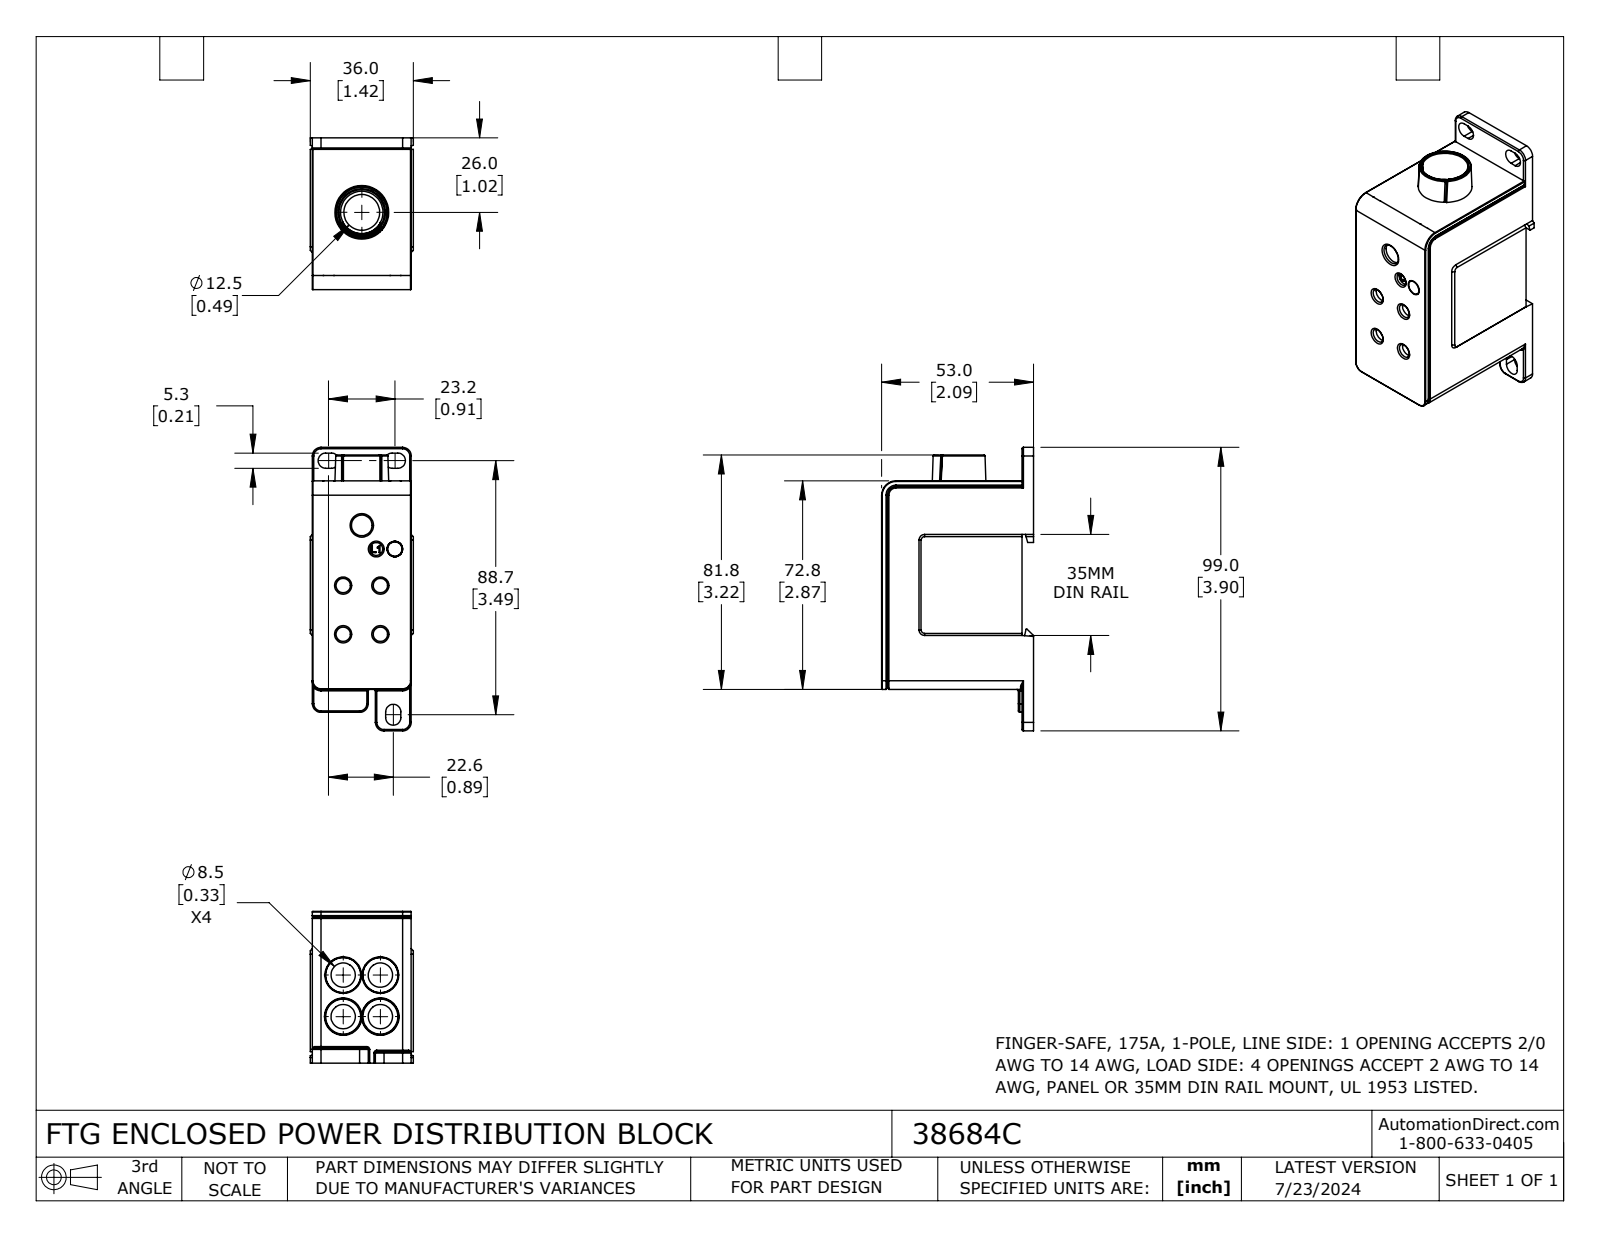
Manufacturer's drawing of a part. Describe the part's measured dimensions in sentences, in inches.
The part is named "38684C". Its 3-D file was written by "SolidWorks 2023 (CONFIG_CONTROL_DESIGN)". It is 1 solid with 276 faces: 92 planar, 72 cylindrical and 112 other. Overall it measures 3.898 by 2.087 by 1.417 inches. Its volume is 7.104 cubic inches and its surface area 39.29 square inches. Round holes: 4 of diameter 0.197, 4 of diameter 0.335, 1 of diameter 0.177, 1 of diameter 0.201, 1 of diameter 0.213, 1 of diameter 0.283, 1 of diameter 0.492, 1 of diameter 0.583. Round bosses or shafts: 1 of diameter 0.197. Partial cylindrical surfaces (rounded edges, fillets, slot ends): 12 of radius 0.02, 8 of radius 0.118, 6 of radius 0.104, 5 of radius 0.008, 4 of radius 0.012, 1 of radius 0.012, 1 of radius 0.197. The main face-to-face distances are 0.03, 1.388, 1.358, 2.087, 0.157, 1.929, 1.417, 2.866, 0.02, 0.209. The hole center spacings are 0.512, 0.317, 0.461, 0.571, 0.669, 0.767, 0.843, 0.865.
